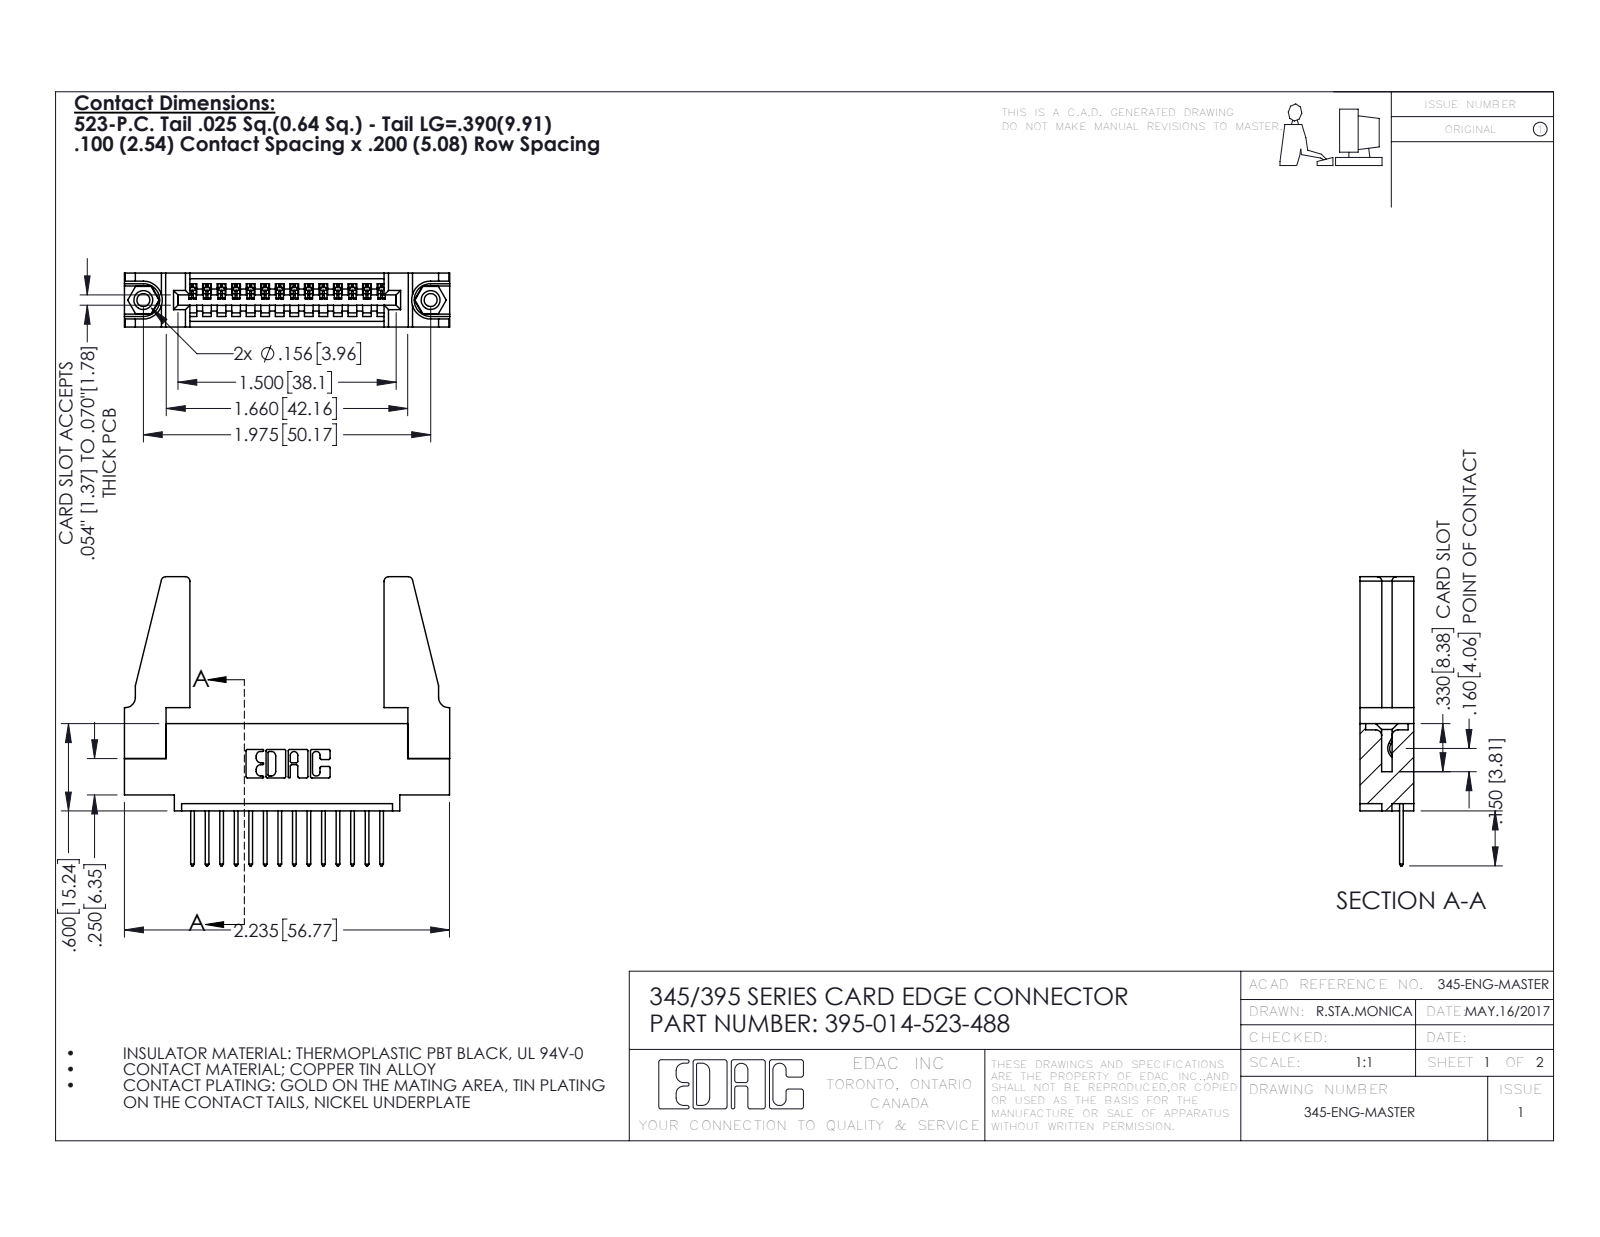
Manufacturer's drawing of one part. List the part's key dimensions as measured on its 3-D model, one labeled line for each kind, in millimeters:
Part name (STEP PRODUCT): 345-292-001_345-293-123; 345 Part_0.110 Offset - 0.156 Dia-TH; 395-014-523-488; 345-250-001_345-250-001-102 (+1 more)
STEP written by: SolidWorks 2016 (CONFIG_CONTROL_DESIGN)
Units: millimetres
Bodies: 19 solids, 1066 faces (716 planar, 334 cylindrical, 16 other)
Overall size (bounding box): 56.8 × 50.5 × 9.4
Volume: 8 340 mm³ · Surface area: 9 606 mm²
Round holes (diameter × count): ⌀2.3 ×2, ⌀3.2 ×2, ⌀4 ×2, ⌀1.6 ×1
Round bosses / shafts (diameter × count): ⌀3.9 ×2
Partial cylindrical surfaces — rounded edges, fillets, slot ends (radius × count): R0.2 ×28, R0.3 ×28, R0.3 ×22, R0.8 ×8, R0.2 ×6, R0.8 ×6, R0.7 ×3, R0.8 ×2
Main face-to-face distances: 9.4, 1.8, 7.6, 5.1, 2.5, 6.9, 0.6, 5.7, 3.8, 3.8
Hole centre spacings: 6.9, 44.2, 50.2
